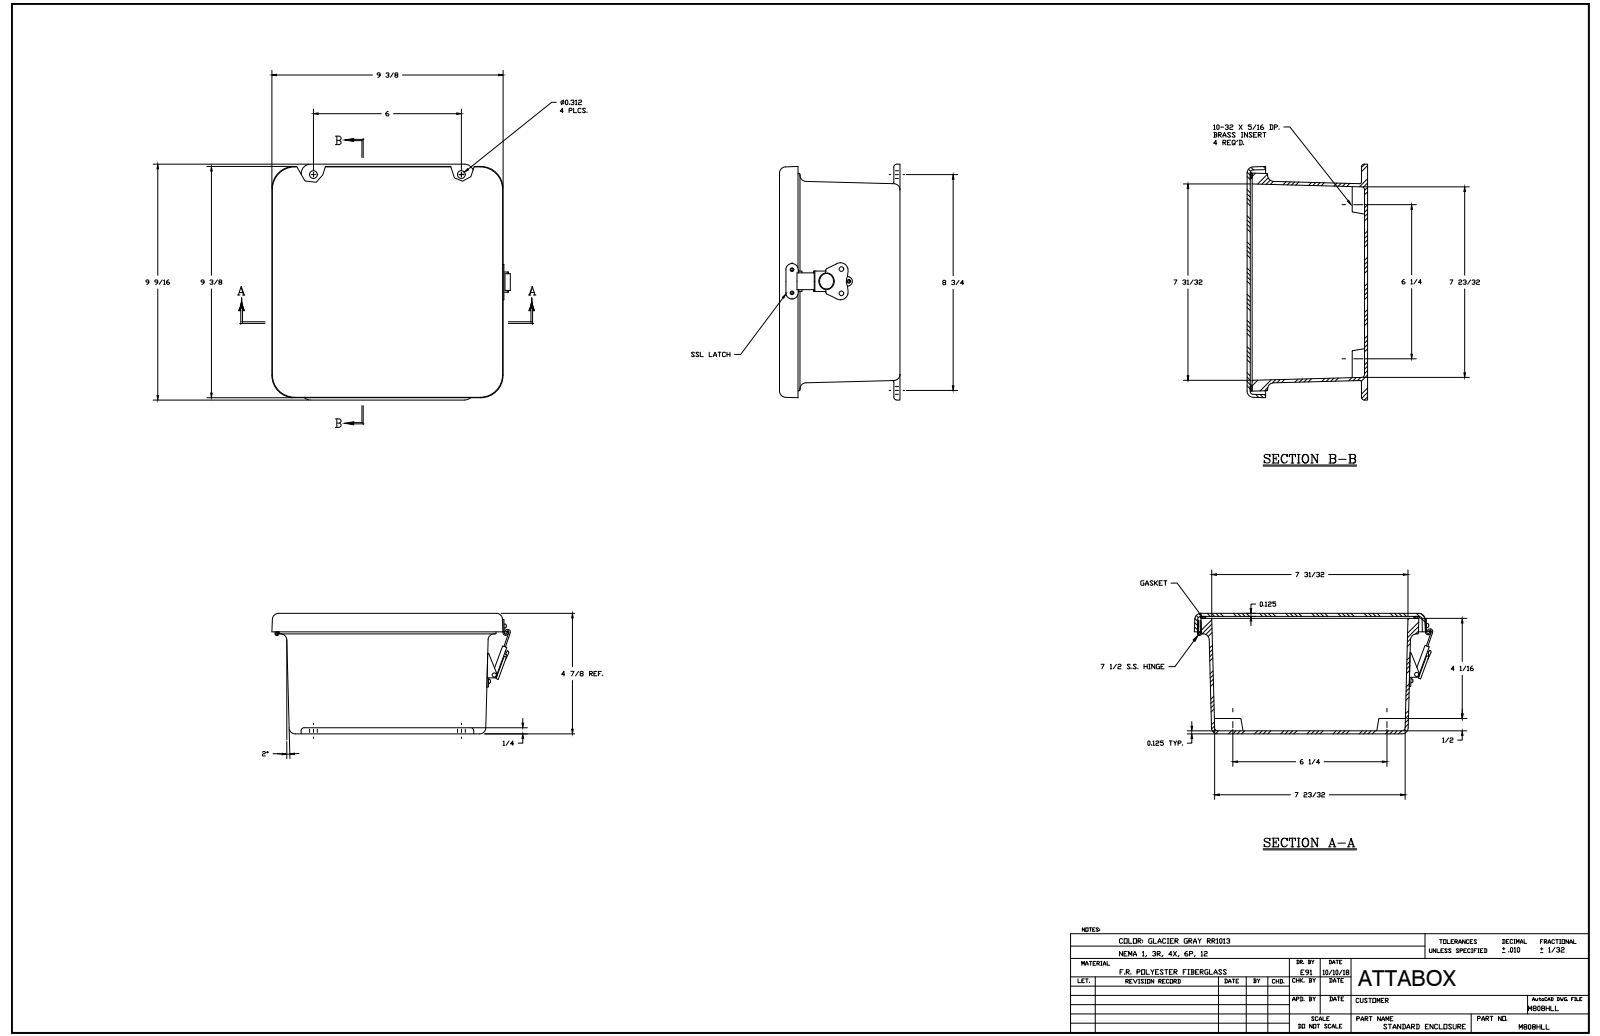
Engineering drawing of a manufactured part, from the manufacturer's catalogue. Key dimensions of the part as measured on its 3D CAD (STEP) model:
Part name (STEP PRODUCT): M808HLL
STEP written by: SolidWorks 2018 (AUTOMOTIVE_DESIGN)
Units: inches
Bodies: 31 solids, 860 faces (336 planar, 329 cylindrical, 195 other)
Overall size (bounding box): 9.598 × 9.562 × 4.887
Volume: 51.77 in³ · Surface area: 749.9 in²
Round holes (diameter × count): ⌀0.14 ×10, ⌀0.152 ×8, ⌀0.131 ×6, ⌀0.156 ×4, ⌀0.218 ×4, ⌀0.13 ×2, ⌀0.165 ×2, ⌀0.197 ×2, ⌀0.085 ×1, ⌀0.085 ×1, ⌀0.106 ×1, ⌀0.118 ×1
Round bosses / shafts (diameter × count): ⌀0.25 ×10, ⌀0.125 ×7, ⌀0.27 ×4, ⌀0.125 ×3, ⌀0.583 ×1, ⌀0.524 ×1, ⌀0.209 ×1, ⌀0.185 ×1
Partial cylindrical surfaces — rounded edges, fillets, slot ends (radius × count): R0.031 ×36, R0.125 ×12, R0.25 ×12, R0.079 ×10, R0.2 ×6, R0.031 ×4, R0.037 ×4, R0.039 ×4
Main face-to-face distances: 0.125, 4.762, 0.125, 4.887, 4.637, 4.685, 4.56, 0.077, 0.202, 0.1
Hole centre spacings: 7.249, 3.5, 1.326, 6.25, 8.125, 10.165, 0.25, 3.25
